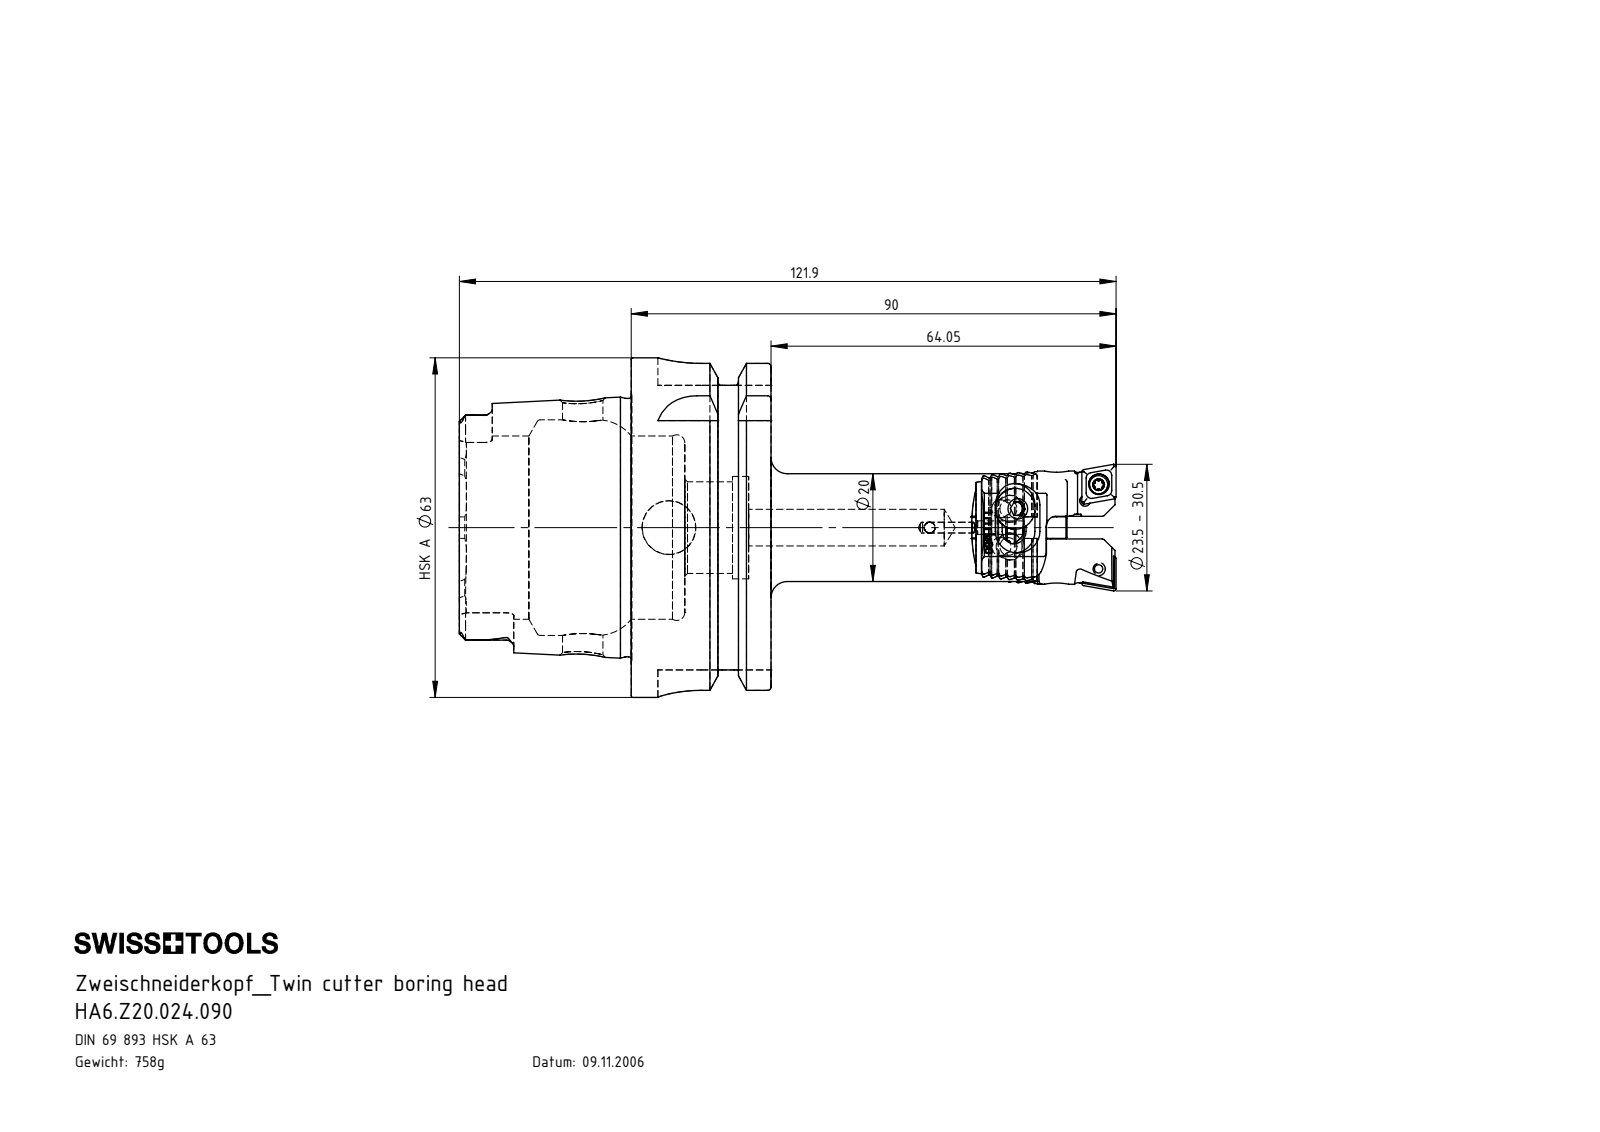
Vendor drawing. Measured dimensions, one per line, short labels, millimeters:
name: HA6.Z20.K23.090; Z20-ER2.001.013_A; Z20-ER1.001.008; Z20-ER1.002.008_A (+2 more)
written by: SolidWorks 2017 (AUTOMOTIVE_DESIGN)
unit: mm
bodies: 6 solids, 359 faces (194 planar, 88 cylindrical, 77 other)
size: 112.8 × 63 × 63
volume: 93 882 mm³; area: 27 111 mm²
holes: 4× ⌀2, 2× ⌀3.3, 2× ⌀4.3, 2× ⌀5, 1× ⌀2.5, 1× ⌀6.8, 1× ⌀7.5, 1× ⌀10, 1× ⌀17, 1× ⌀19, 1× ⌀34, 1× ⌀40
bosses: 3× ⌀4, 2× ⌀7.6, 2× ⌀7.2, 1× ⌀63, 1× ⌀54.95, 1× ⌀47.94, 1× ⌀20, 1× ⌀3
rounds: 14× R0.12, 6× R1.4, 4× R2.88, 4× R8, 2× R220
face distances: 25.95, 16, 9.95, 31.9, 41.85, 57.85, 21.8, 52.8, 1.43, 11.85
hole spacings: 48.4
